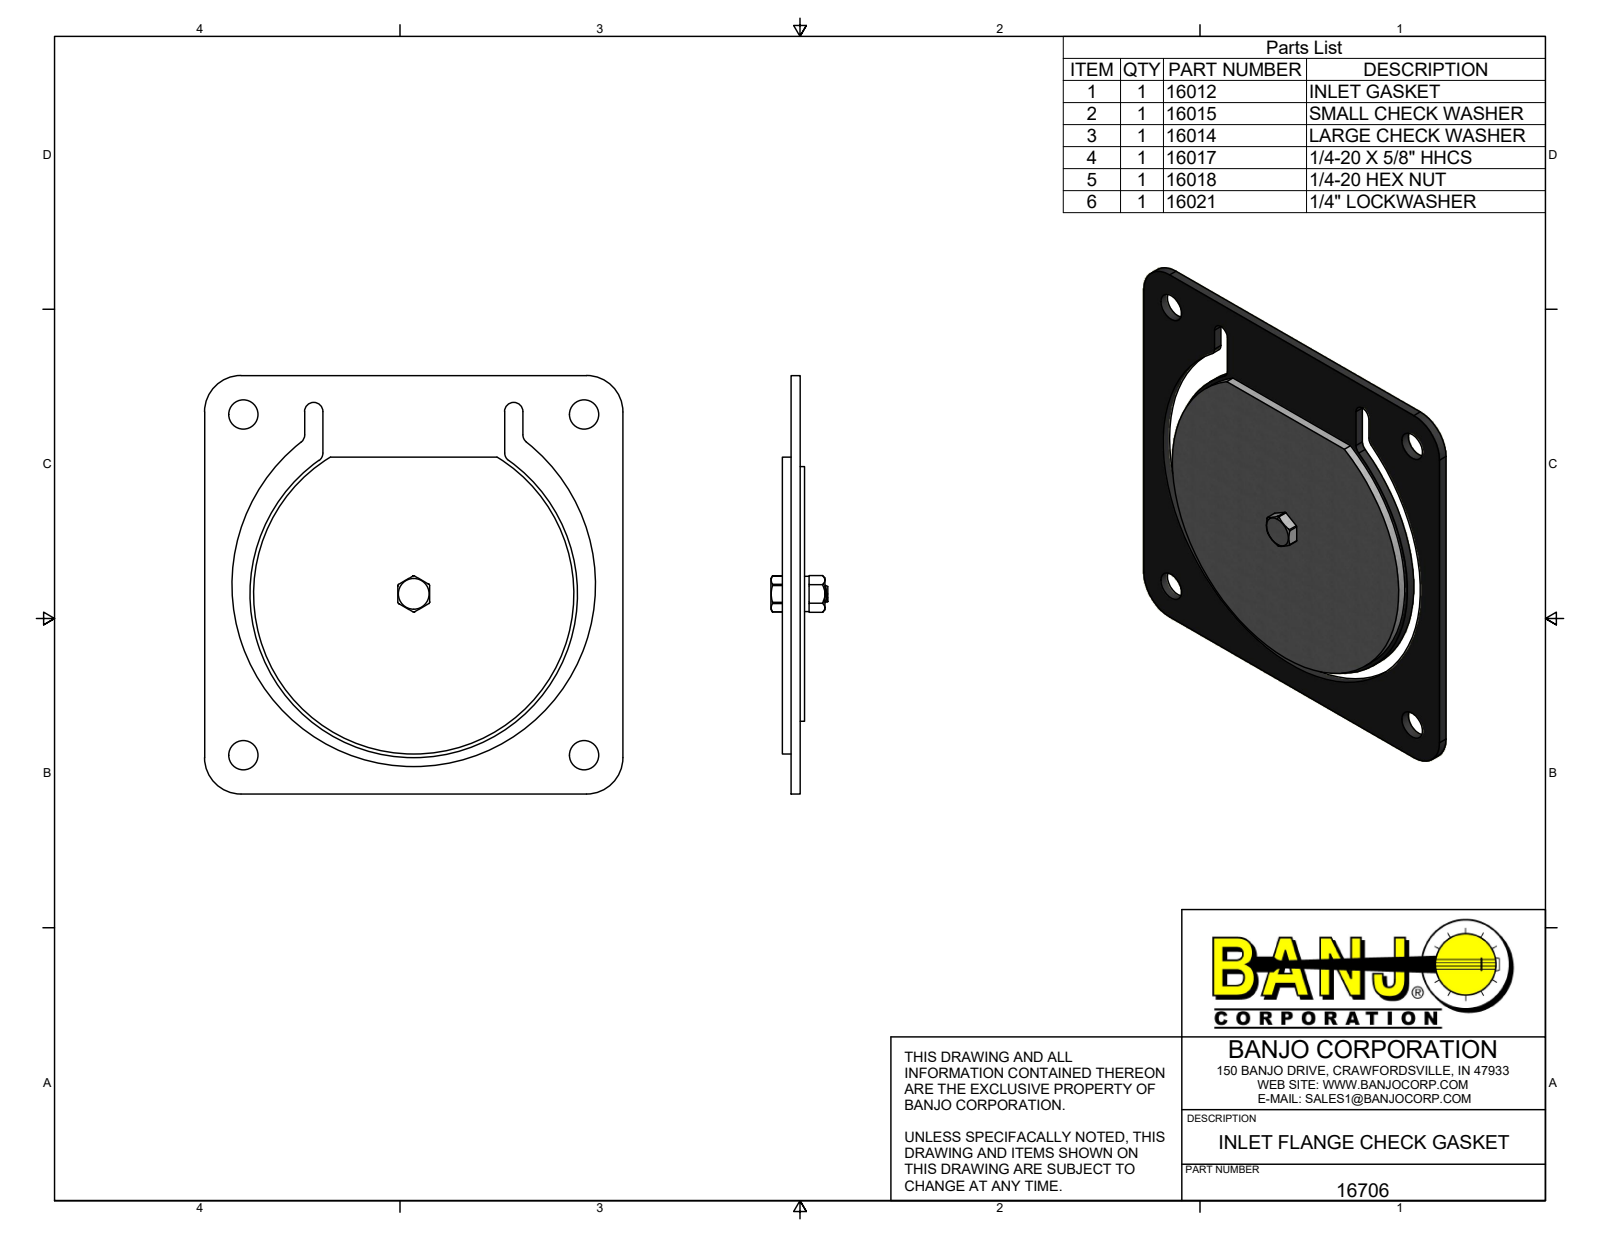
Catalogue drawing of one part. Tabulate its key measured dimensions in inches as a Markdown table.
| quantity | value |
| --- | --- |
| part name | 16706; 16012; 16015; 16014 (+3 more) |
| STEP written by | Autodesk Inventor 2017 (AUTOMOTIVE_DESIGN) |
| units | inches |
| bodies | 6 solids, 225 faces (37 planar, 99 cylindrical, 89 other) |
| overall size | 5.75 × 5.75 × 0.781 |
| volume | 6.086 in³ |
| surface area | 118.8 in² |
| round holes (diameter × count) | 0.4 × 4, 0.196 × 1, 0.26 × 1, 0.28 × 1 |
| round bosses / shafts (diameter × count) | 0.212 × 12, 4.5 × 1, 4.4 × 1, 3.5 × 1, 0.487 × 1, 0.25 × 1 |
| partial cylindrical surfaces (radius × count) | 0.125 × 6, 0.5 × 4, 0.106 × 1, 0.248 × 1, 2.5 × 1 |
| main face-to-face distances | 0.125, 0.245, 0.12, 0.06, 0.185, 0.305, 5.75, 4.63, 1.12, 0.437 |
| hole center spacings | 4.685, 6.625, 3.225, 3.226, 3.402, 3.402 |
